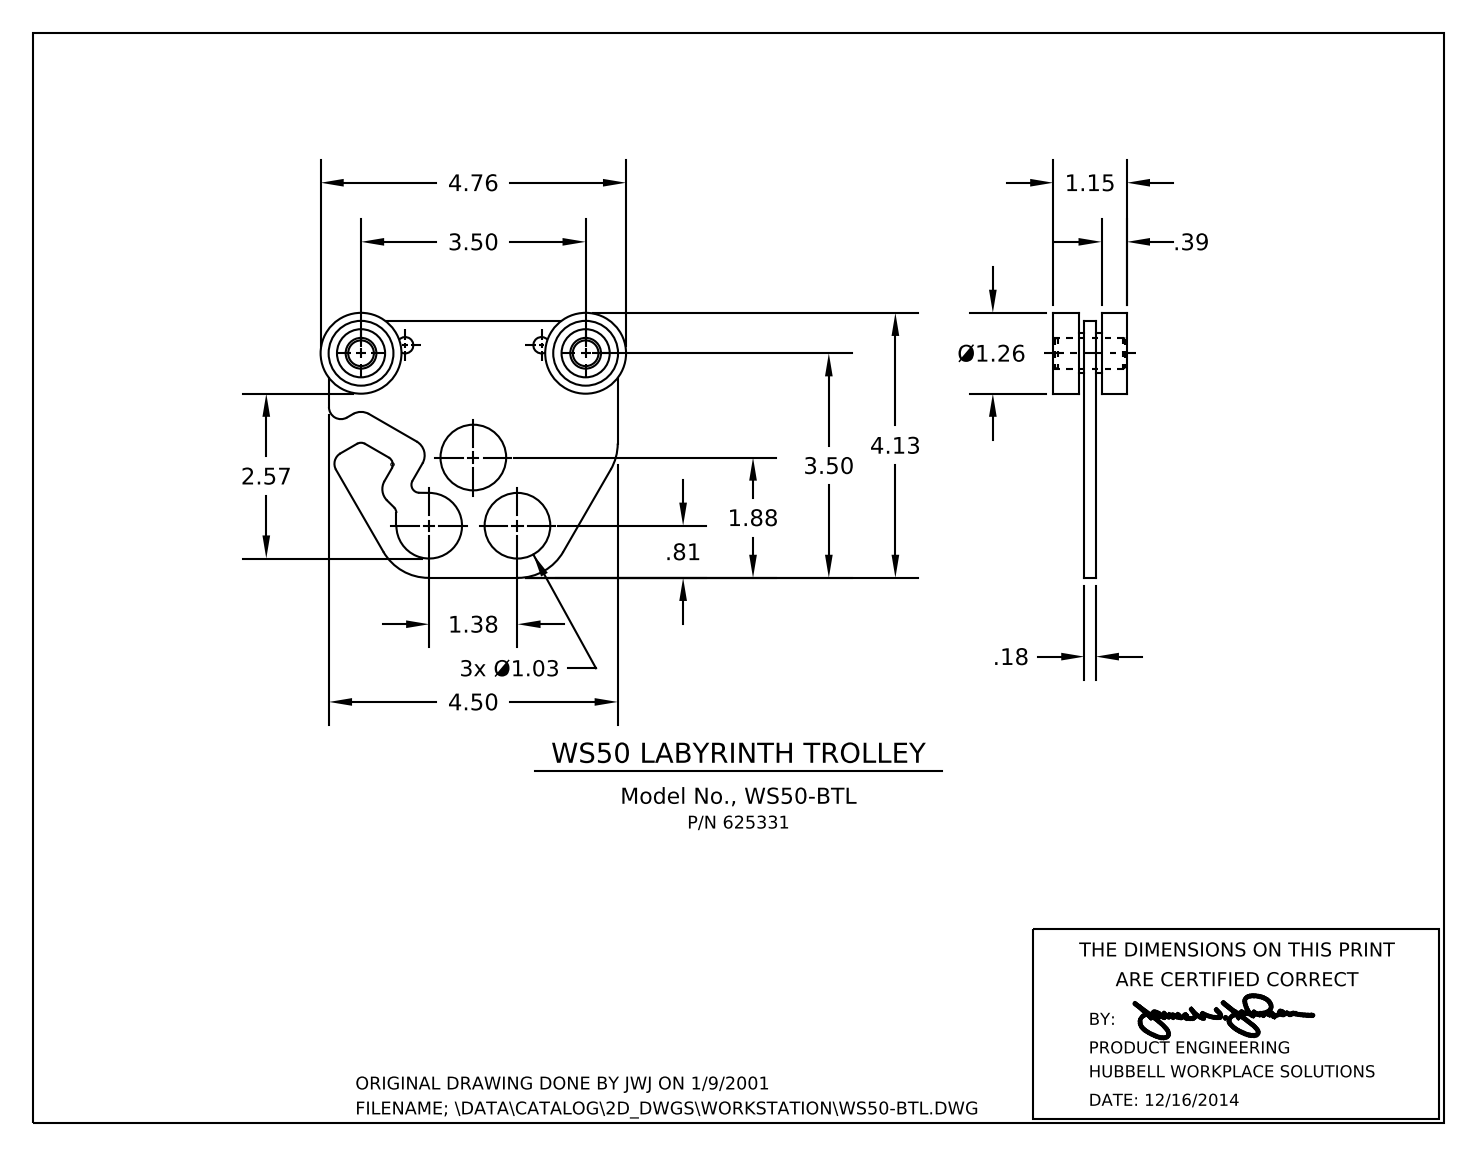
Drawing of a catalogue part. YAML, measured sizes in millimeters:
part_name: "625331"
step_written_by: "Autodesk Inventor 2013 (AUTOMOTIVE_DESIGN)"
units: millimeters
bodies: {solids: 11, faces: 344, planar: 77, cylindrical: 79, other: 188}
overall_size: [120.9, 104.9, 29.1]
volume: 64450
surface_area: 47140
round_holes:
  - {diameter: 6.5, count: 2}
  - {diameter: 12, count: 2}
  - {diameter: 12.2, count: 2}
  - {diameter: 12.3, count: 2}
  - {diameter: 18.7, count: 2}
  - {diameter: 20.5, count: 2}
  - {diameter: 25.5, count: 2}
  - {diameter: 26.2, count: 2}
round_bosses_or_shafts:
  - {diameter: 32, count: 2}
  - {diameter: 23.5, count: 2}
  - {diameter: 18.5, count: 2}
  - {diameter: 15.9, count: 2}
  - {diameter: 12, count: 2}
partial_cylinders:
  - {radius: 3.2, count: 4}
  - {radius: 6.4, count: 3}
  - {radius: 20.6, count: 3}
  - {radius: 4.8, count: 2}
  - {radius: 12.7, count: 2}
  - {radius: 13.1, count: 1}
face_to_face_distances: [4.5, 19.1, 10, 8.4, 10.7, 15.3, 1.5, 1.6, 6.9, 8.4]
hole_center_spacings: [60.7, 17.7, 17.8, 32.1, 52, 52, 54, 71.5]
